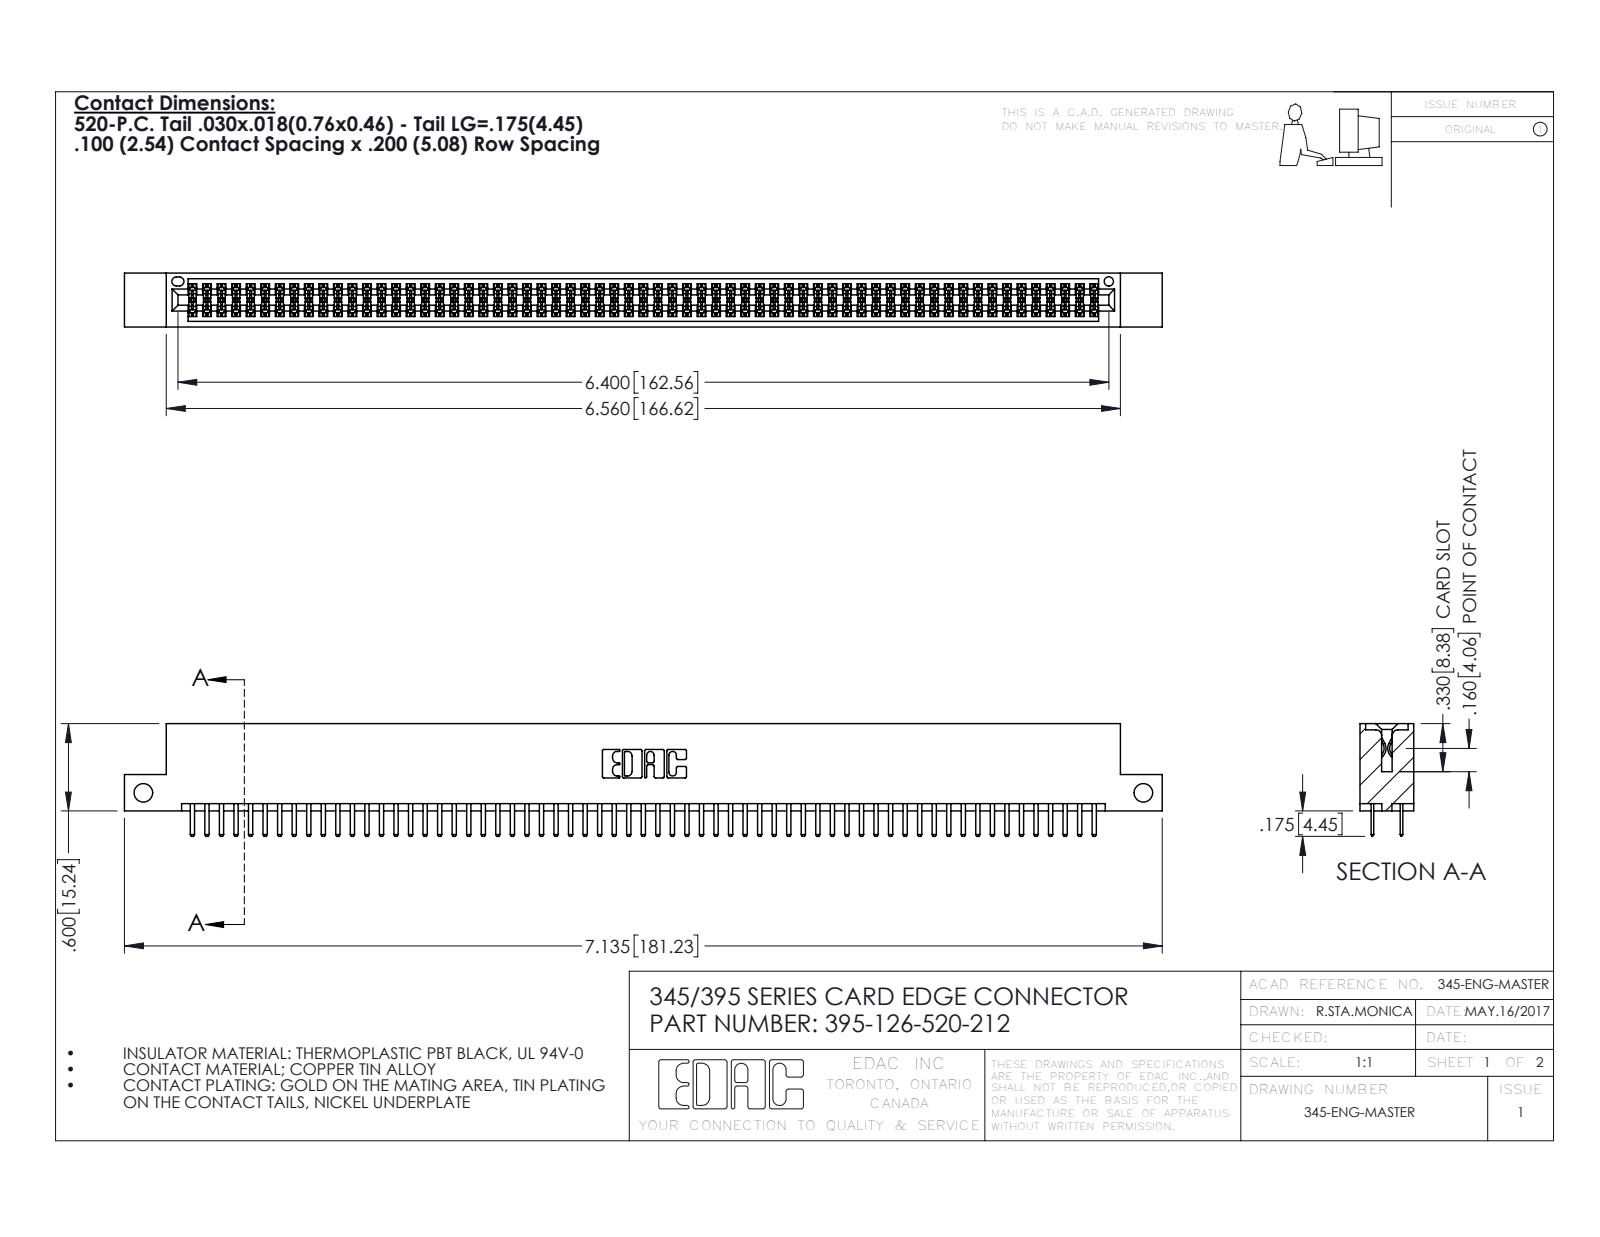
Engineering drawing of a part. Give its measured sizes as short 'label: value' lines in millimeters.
name: 345-292-001_345-293-120; 395-126-520-212; 345 Part_Flush Mounting Lugs - Side Mount
written by: SolidWorks 2016 (CONFIG_CONTROL_DESIGN)
unit: mm
bodies: 127 solids, 6930 faces (4490 planar, 2440 cylindrical, 0 other)
size: 181.2 × 19.7 × 9.4
volume: 17 650 mm³; area: 26 250 mm²
holes: 2× ⌀3.3, 1× ⌀1.6
rounds: 189× R0.2, 130× R0.3, 22× R0.3, 6× R0.2, 6× R0.8, 3× R0.7, 2× R0.4, 2× R0.5
face distances: 7.6, 1.8, 5.1, 9.4, 2.5, 6.9, 0.6, 5.7, 0.6, 1.8
hole spacings: 174.6
